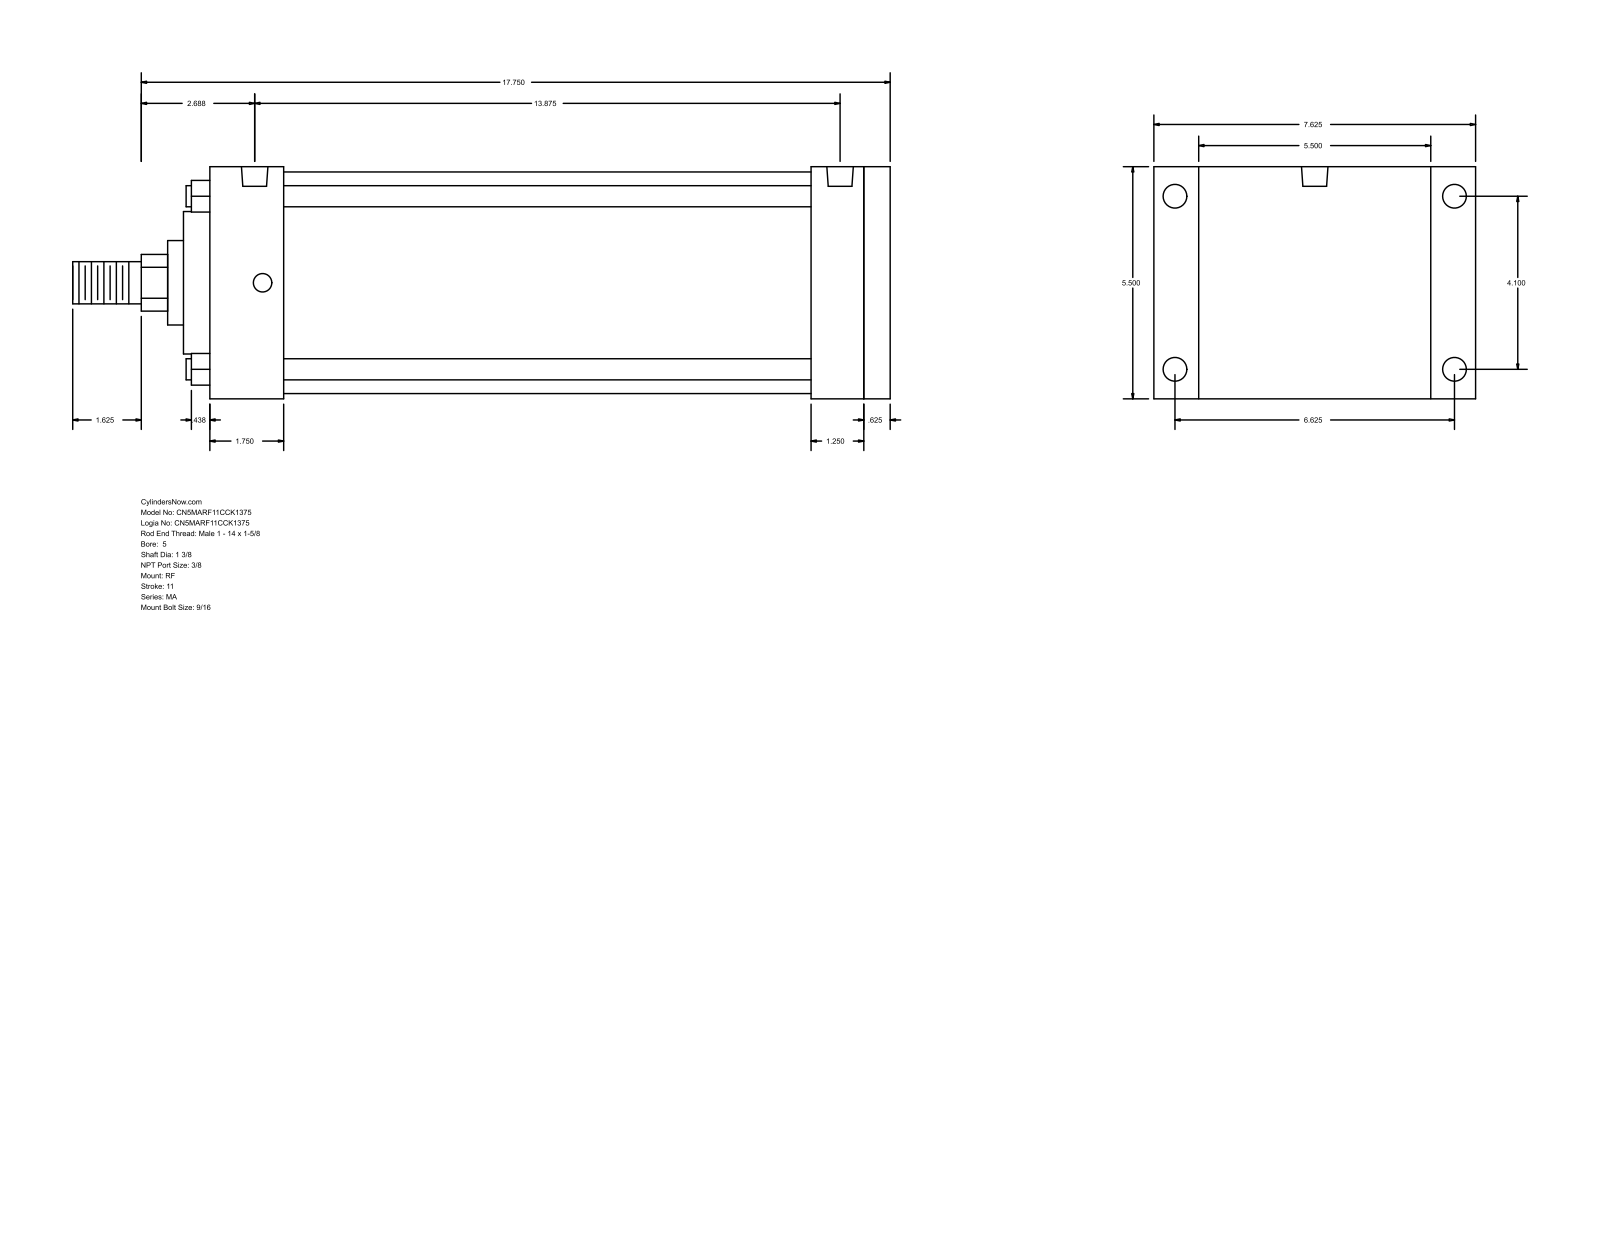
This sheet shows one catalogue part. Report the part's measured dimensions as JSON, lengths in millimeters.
{"part_name": "MA_RF__0500_1.375", "step_written_by": "GSSL Pune (CONFIG_CONTROL_DESIGN)", "units": "millimeters", "bodies": {"solids": 0, "faces": 94, "planar": 65, "cylindrical": 29, "other": 0}, "overall_size": [492.12, 193.68, 139.7], "round_holes": [[11.11, 4], [14.29, 4], [15.93, 2]], "round_bosses_or_shafts": [[12.7, 4], [133.35, 1], [85.72, 1], [50.8, 1], [34.92, 1], [25.4, 1]], "partial_cylinders_radius": [[17.06, 1]], "face_to_face_distances": [139.7, 409.58, 15.87, 393.71, 44.45, 349.26, 365.13, 361.96, 317.51, 31.75], "hole_center_spacings": [104.14, 168.28, 197.9, 342.9, 4.76, 4.77, 347.66, 347.67]}
